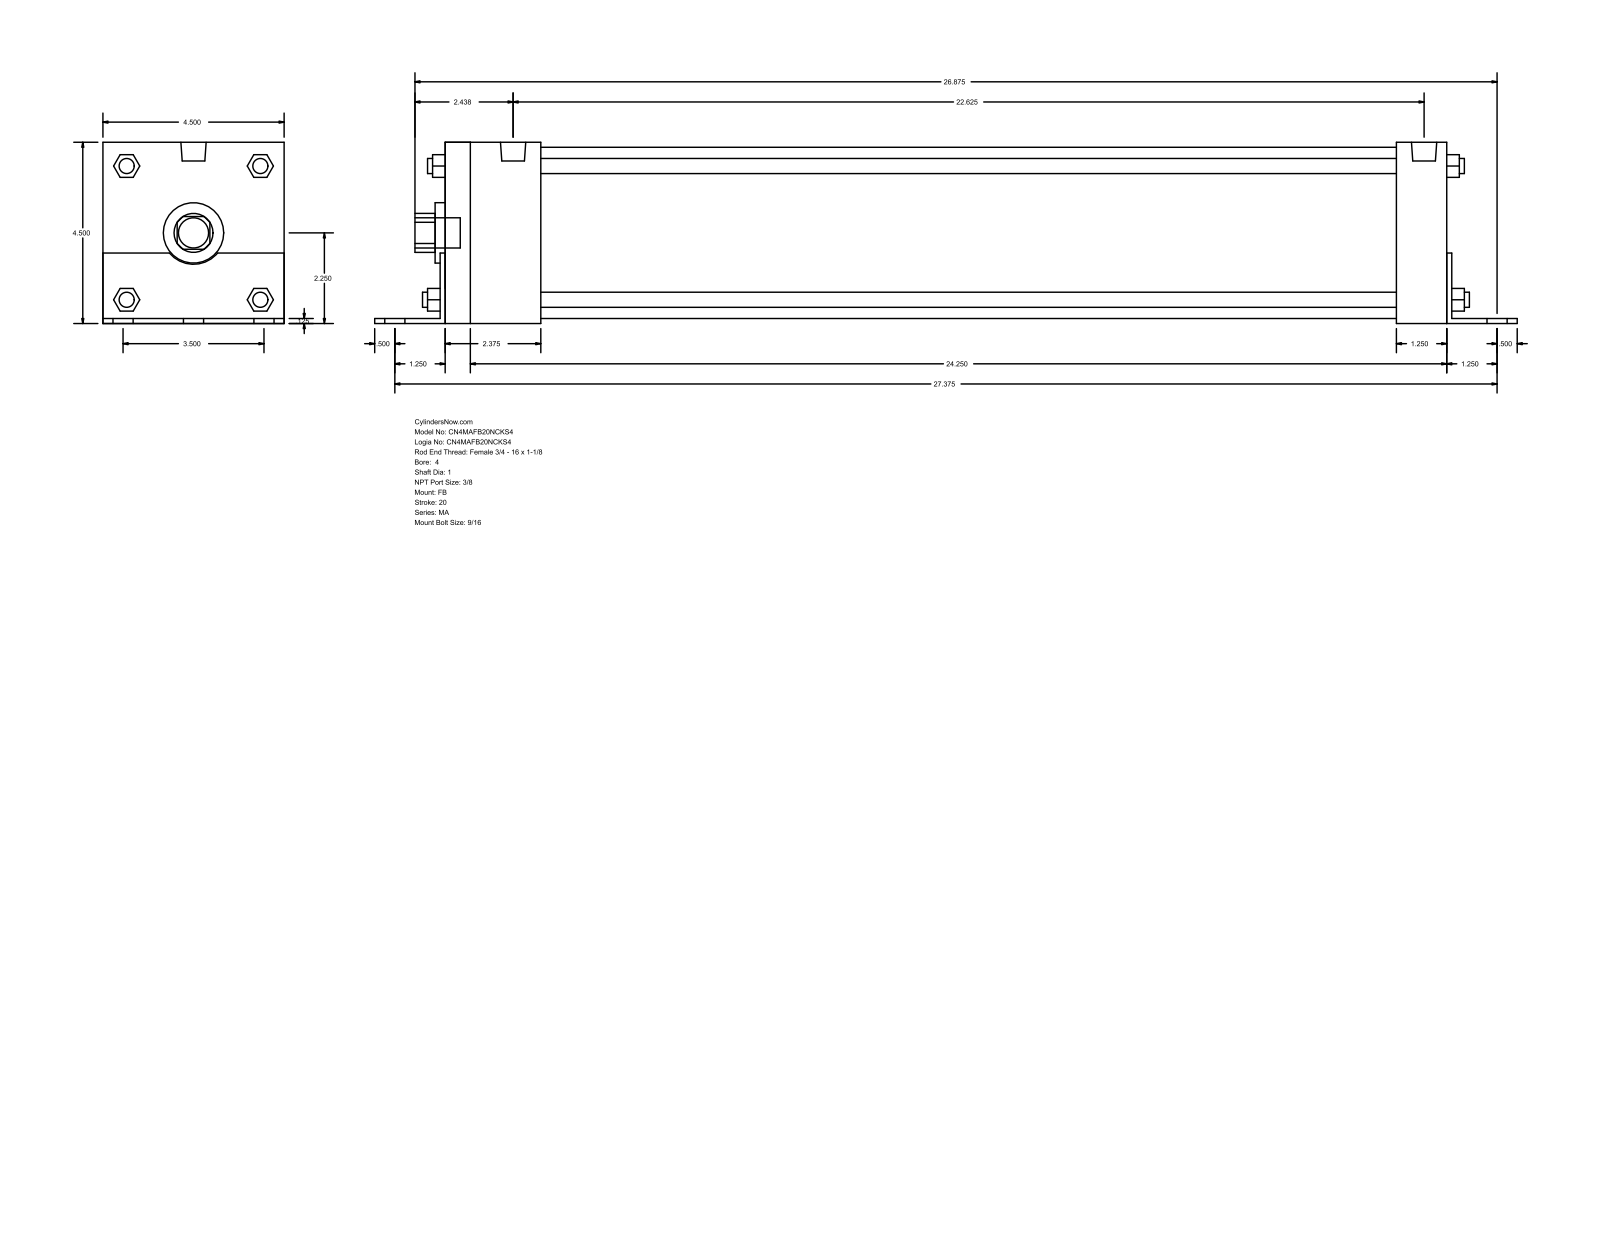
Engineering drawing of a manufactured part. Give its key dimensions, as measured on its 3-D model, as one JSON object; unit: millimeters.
{"part_name": "MA_FB__0400_1", "step_written_by": "GSSL Pune (CONFIG_CONTROL_DESIGN)", "units": "millimeters", "bodies": {"solids": 0, "faces": 140, "planar": 105, "cylindrical": 35, "other": 0}, "overall_size": [720.73, 114.35, 114.3], "round_holes": [[25.4, 1], [38.1, 1], [107.95, 1]], "round_bosses_or_shafts": [[14.29, 6], [11.11, 4], [9.53, 4], [15.93, 2], [19.05, 1]], "partial_cylinders_radius": [[12.29, 1], [19.81, 1]], "face_to_face_distances": [114.3, 3.17, 114.35, 635, 3.12, 111.18, 631.83, 638.17, 34.93, 603.24]}
